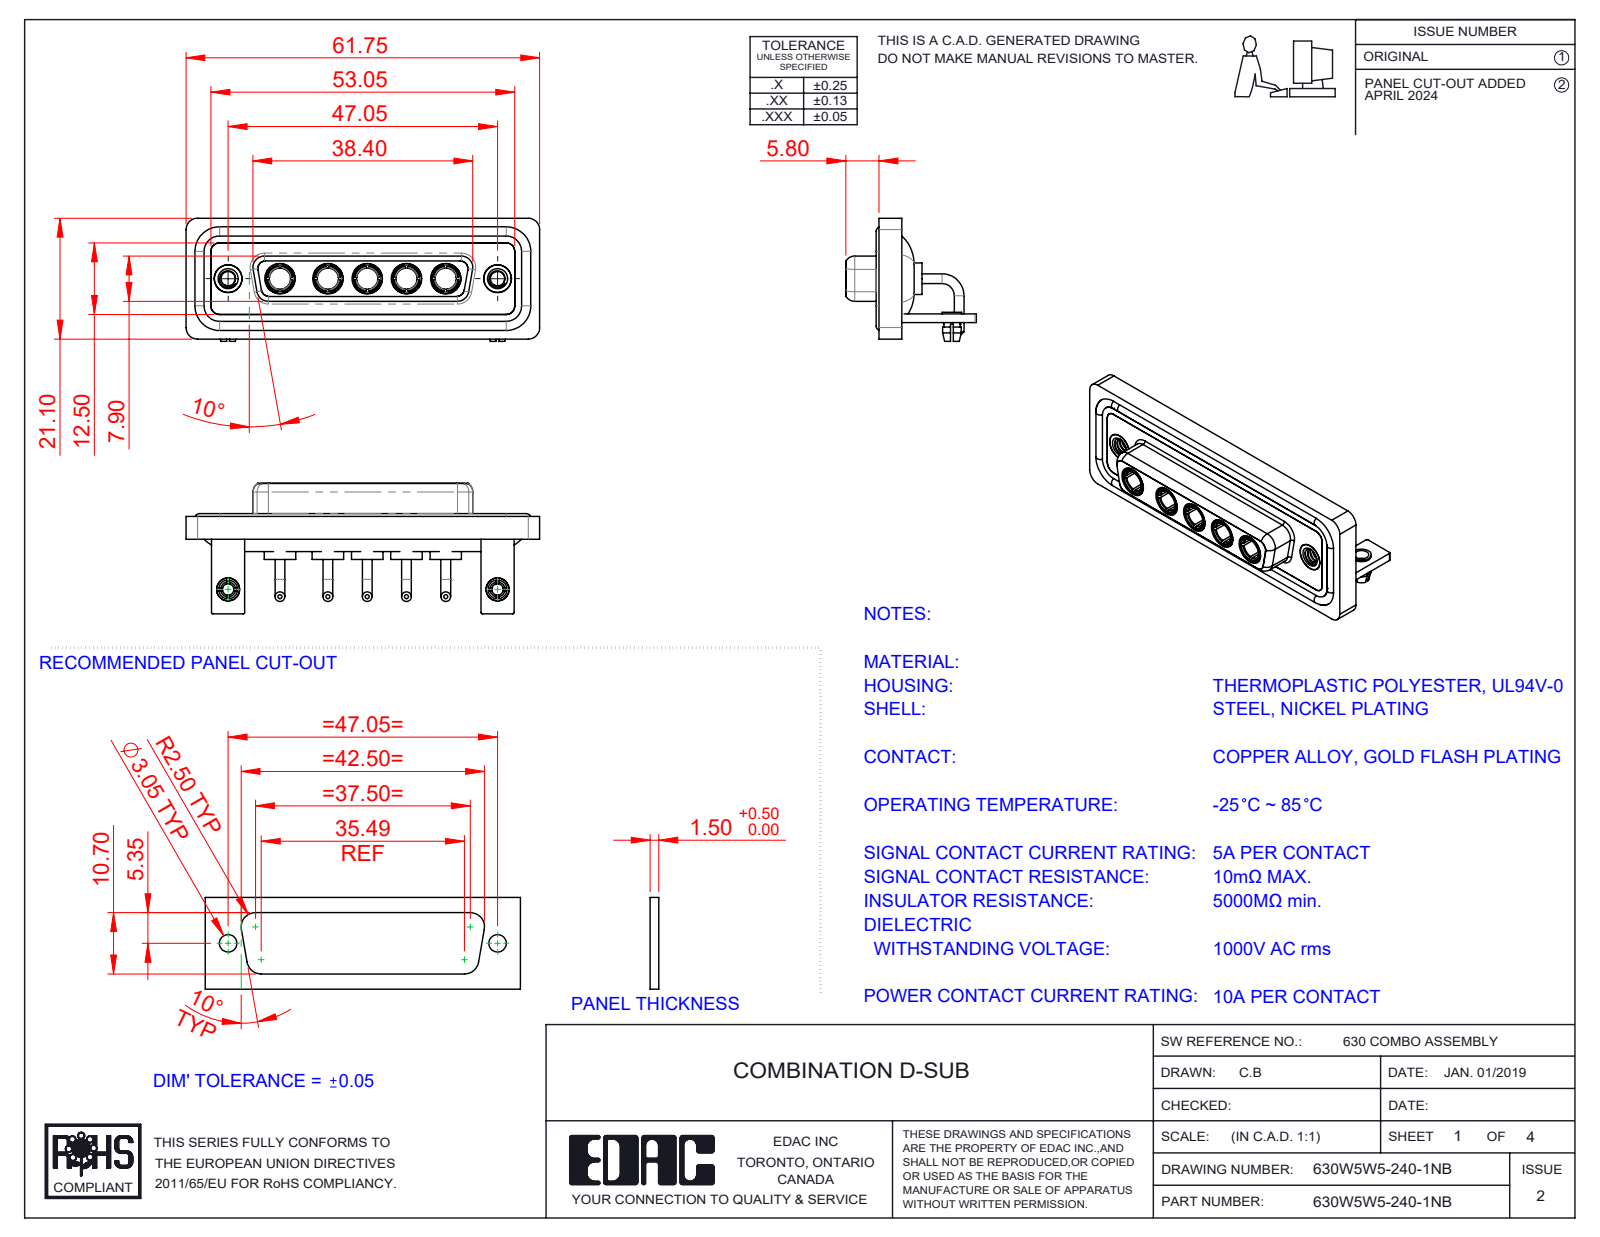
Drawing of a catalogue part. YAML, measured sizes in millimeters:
part_name: "630Combo Stabilizer Bracket_50 Contacts; 630Combo Board Lock_50 Contacts; 630Combo Waterproof Housing_25 Contacts; 630Combo Shell Front_25 Contacts (+5 more)"
step_written_by: "SolidWorks 2023 (CONFIG_CONTROL_DESIGN)"
units: millimeters
bodies: {solids: 21, faces: 910, planar: 318, cylindrical: 367, other: 225}
overall_size: [61.75, 22.8, 21.5]
volume: 8542
surface_area: 14509
round_holes:
  - {diameter: 4.85, count: 7}
  - {diameter: 3.7, count: 5}
  - {diameter: 5.3, count: 5}
  - {diameter: 2.5, count: 4}
  - {diameter: 2, count: 2}
  - {diameter: 3.2, count: 2}
  - {diameter: 4, count: 2}
  - {diameter: 4.05, count: 2}
  - {diameter: 5, count: 2}
round_bosses_or_shafts:
  - {diameter: 1.7, count: 10}
  - {diameter: 5.5, count: 5}
  - {diameter: 5.2, count: 5}
  - {diameter: 4.96, count: 5}
  - {diameter: 4.75, count: 5}
  - {diameter: 3.75, count: 5}
  - {diameter: 1.6, count: 4}
  - {diameter: 4.95, count: 2}
partial_cylinders:
  - {radius: 2, count: 19}
  - {radius: 1.5, count: 18}
  - {radius: 0.25, count: 16}
  - {radius: 1.35, count: 8}
  - {radius: 1.6, count: 8}
  - {radius: 0.5, count: 5}
  - {radius: 2.1, count: 5}
  - {radius: 0.6, count: 4}
face_to_face_distances: [0.4, 1.8, 1.5, 2.9, 3.7, 4.1, 1.1, 1.4, 1.6, 2.5]
hole_center_spacings: [6.86, 9.04, 38.01, 47.05, 6.87, 8.38, 13.72, 13.73]
